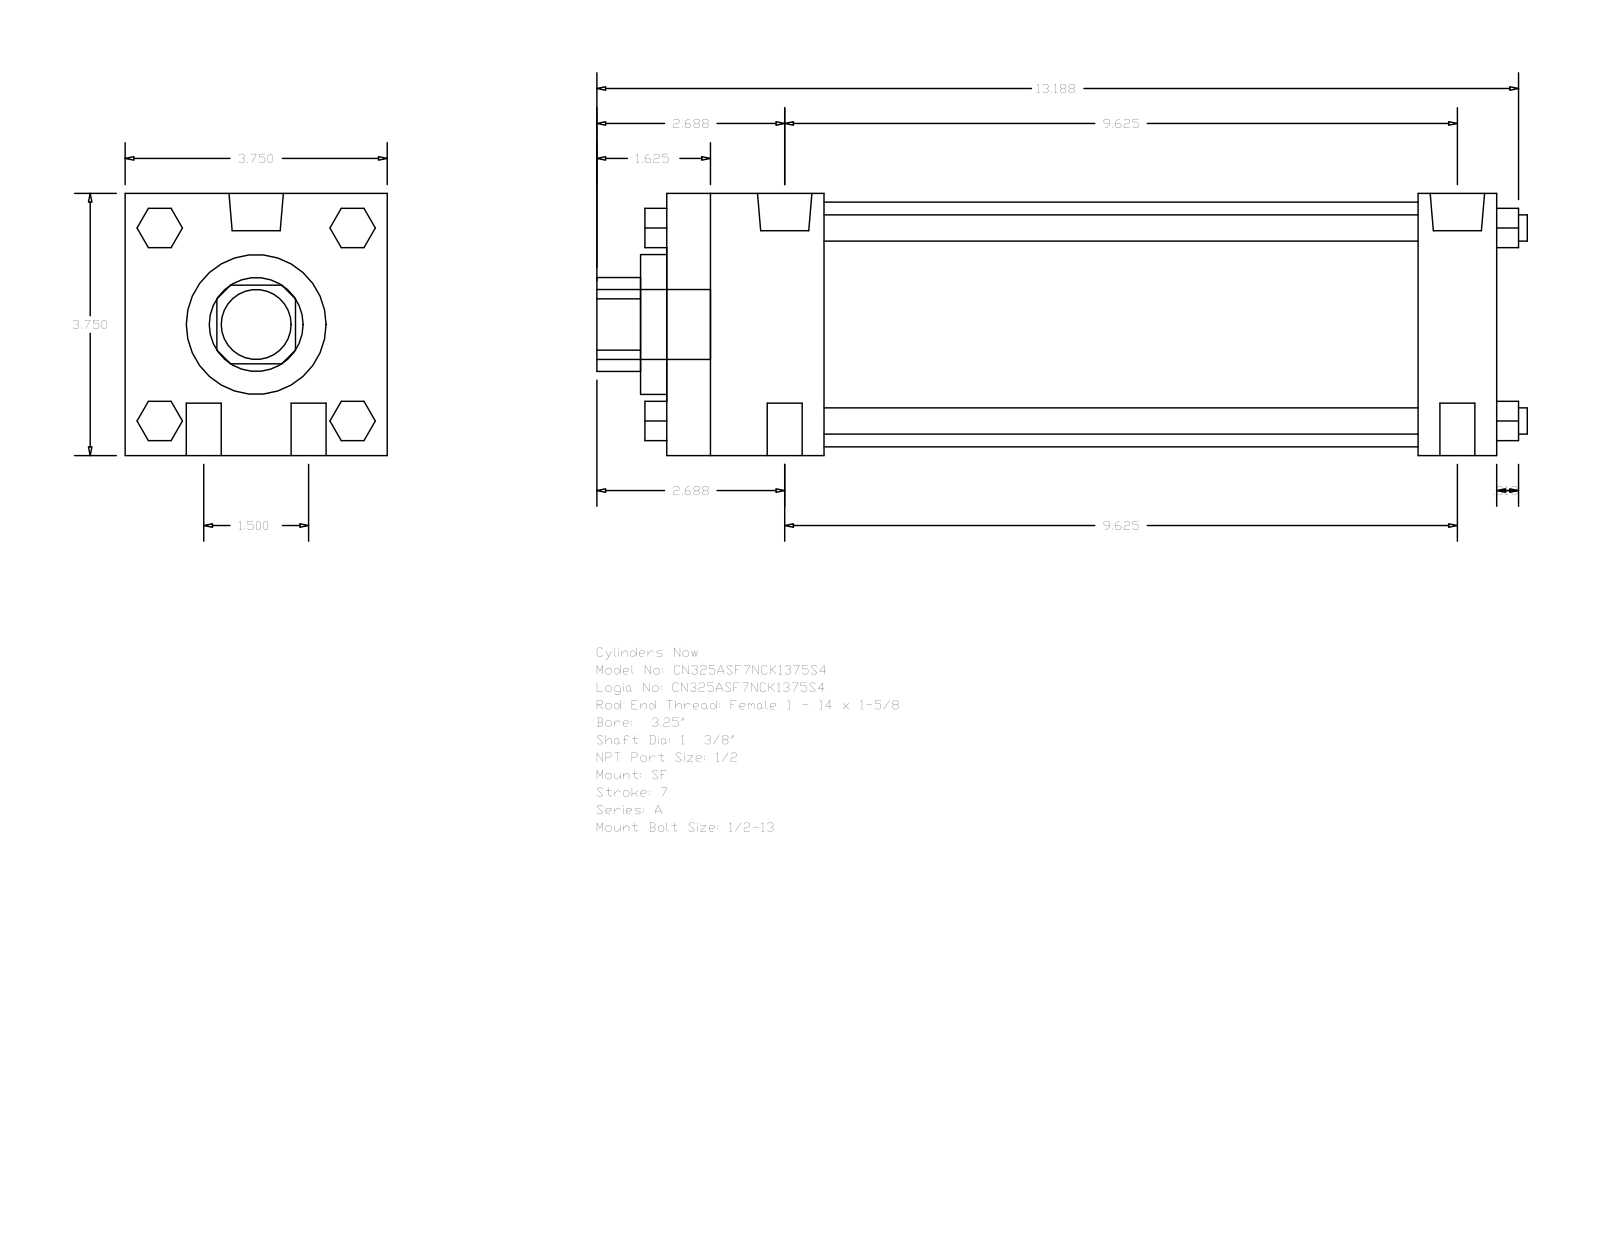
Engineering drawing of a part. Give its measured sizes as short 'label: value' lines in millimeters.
name: A_SF__0325_1.375
written by: GSSL Pune (CONFIG_CONTROL_DESIGN)
unit: mm
bodies: 0 solids, 124 faces (94 planar, 30 cylindrical, 0 other)
size: 338.14 × 95.25 × 95.25
holes: 1× ⌀34.92, 1× ⌀50.8, 1× ⌀88.9
bosses: 4× ⌀12.7, 4× ⌀9.53, 2× ⌀19.77, 2× ⌀8.73, 1× ⌀25.4
rounds: 1× R17.06
face distances: 95.24, 301.62, 28.57, 273.05, 57.15, 215.9, 244.47, 9.52, 66.67, 282.57
